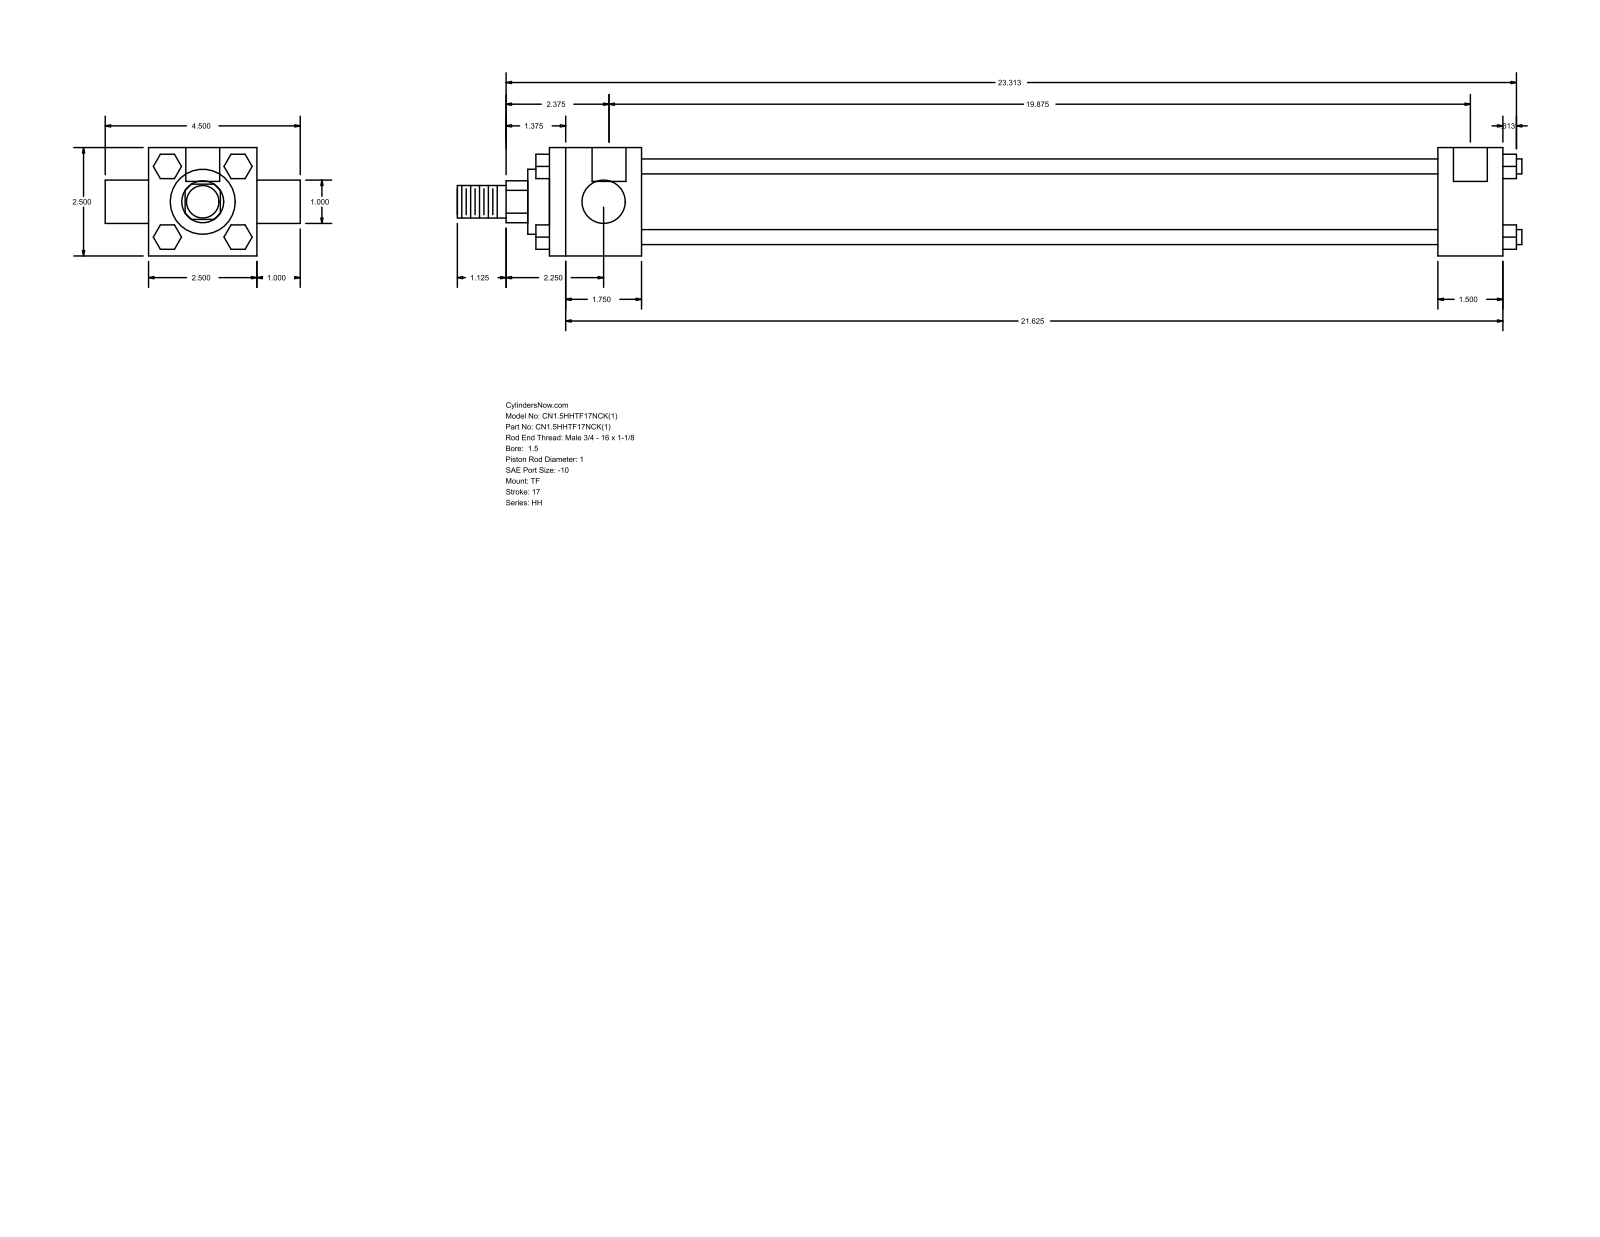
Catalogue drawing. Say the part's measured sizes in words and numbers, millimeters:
The part is named "HH_TF__0150_1". Its 3-D file was written by "GSSL Pune (CONFIG_CONTROL_DESIGN)". It is 0 solids with 120 faces: 92 planar, 28 cylindrical and 0 other. Overall it measures 623.89 by 114.3 by 63.5 millimeters. Round holes: 3 of diameter 5.56, 2 of diameter 19.84. Round bosses or shafts: 4 of diameter 8.76, 2 of diameter 25.4, 1 of diameter 44.45, 1 of diameter 38.1, 1 of diameter 19.05. Partial cylindrical surfaces (rounded edges, fillets, slot ends): 1 of radius 12.29. The main face-to-face distances are 63.5, 38.1, 504.82, 466.72, 53.98, 520.7, 558.8, 25.4, 20.7, 14.29. The hole center spacings are 1.59, 506.41, 504.82, 508.
